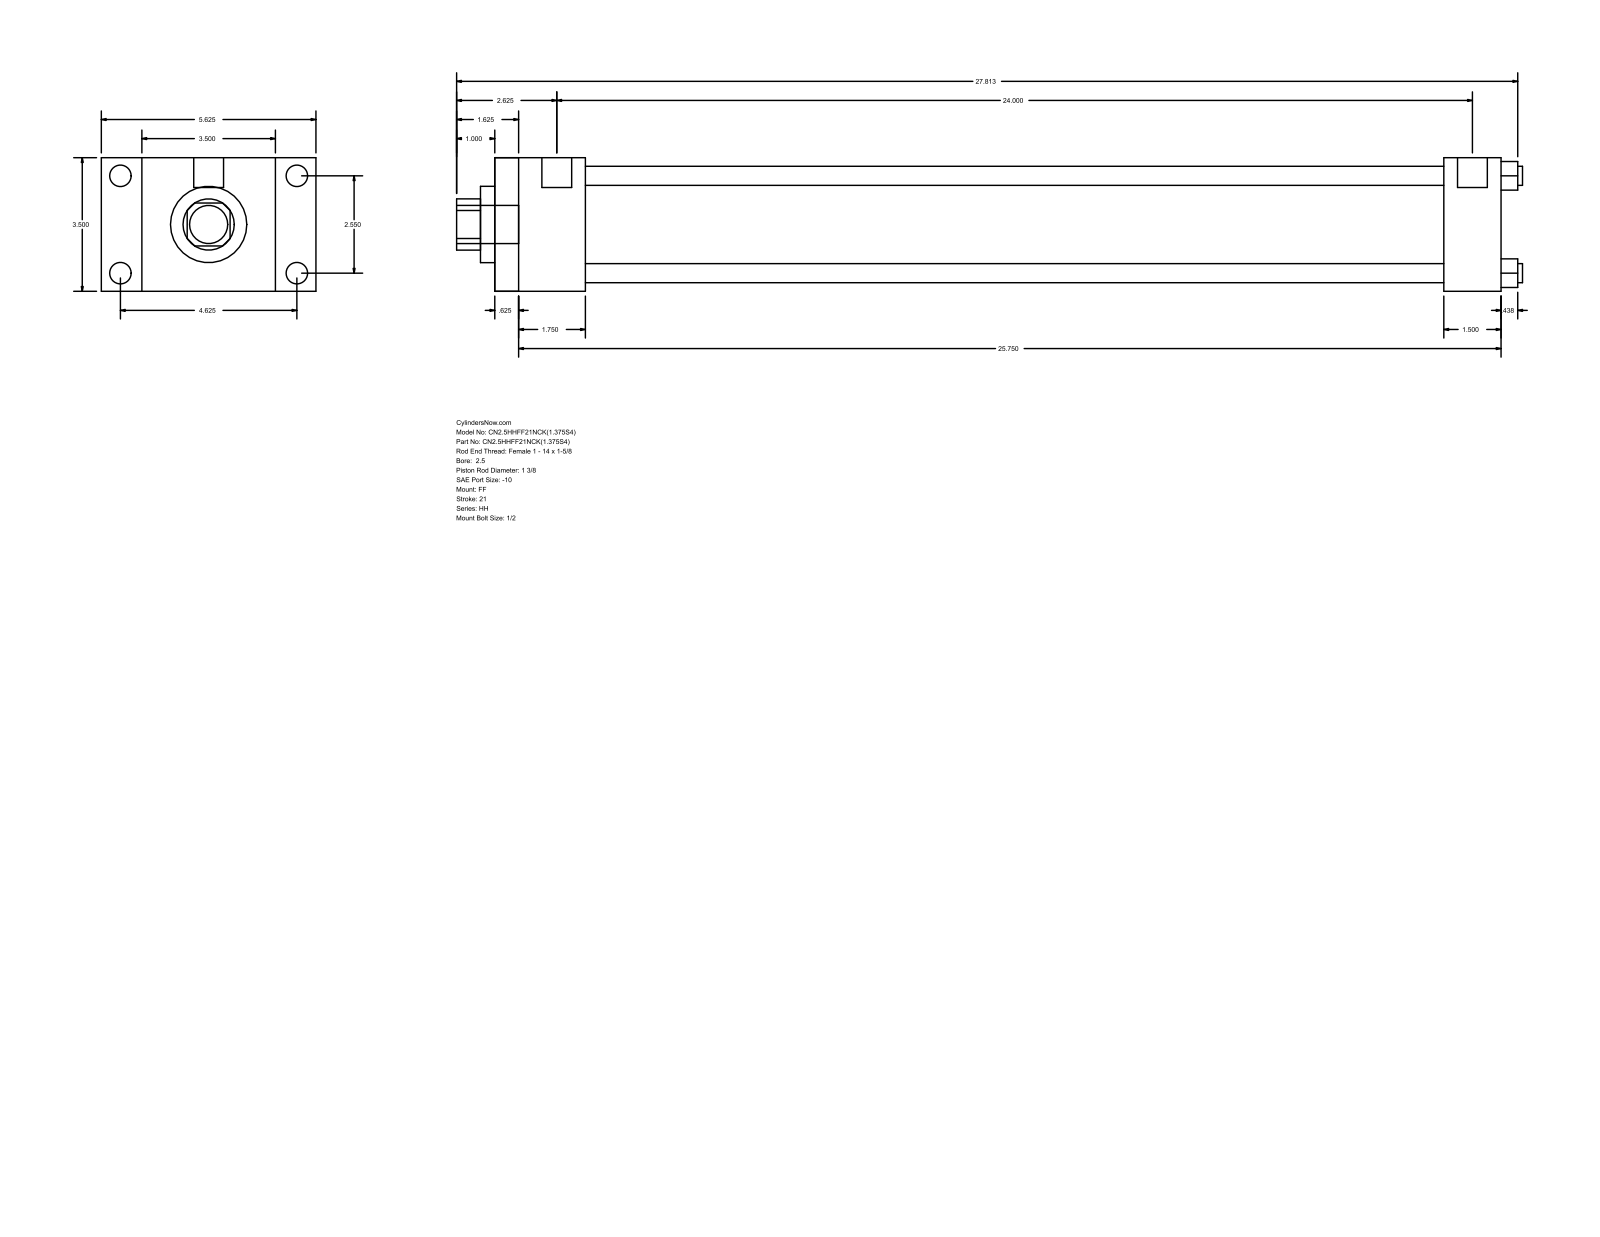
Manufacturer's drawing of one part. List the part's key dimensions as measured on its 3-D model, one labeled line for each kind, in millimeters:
Part name (STEP PRODUCT): HH_FF__0250_1.375
STEP written by: GSSL Pune (CONFIG_CONTROL_DESIGN)
Units: millimetres
Bodies: 0 solids, 92 faces (64 planar, 28 cylindrical, 0 other)
Overall size (bounding box): 709.61 × 142.88 × 88.9
Round holes (diameter × count): ⌀12.7 ×4, ⌀34.92 ×1, ⌀50.8 ×1, ⌀73.03 ×1
Round bosses / shafts (diameter × count): ⌀14.3 ×4, ⌀5.56 ×4, ⌀19.84 ×2, ⌀25.4 ×1
Partial cylindrical surfaces — rounded edges, fillets, slot ends (radius × count): R17.06 ×1
Main face-to-face distances: 88.9, 669.93, 15.87, 654.06, 60.32, 44.45, 609.61, 631.83, 615.96, 571.51
Hole centre spacings: 45.79, 64.76, 91.58
